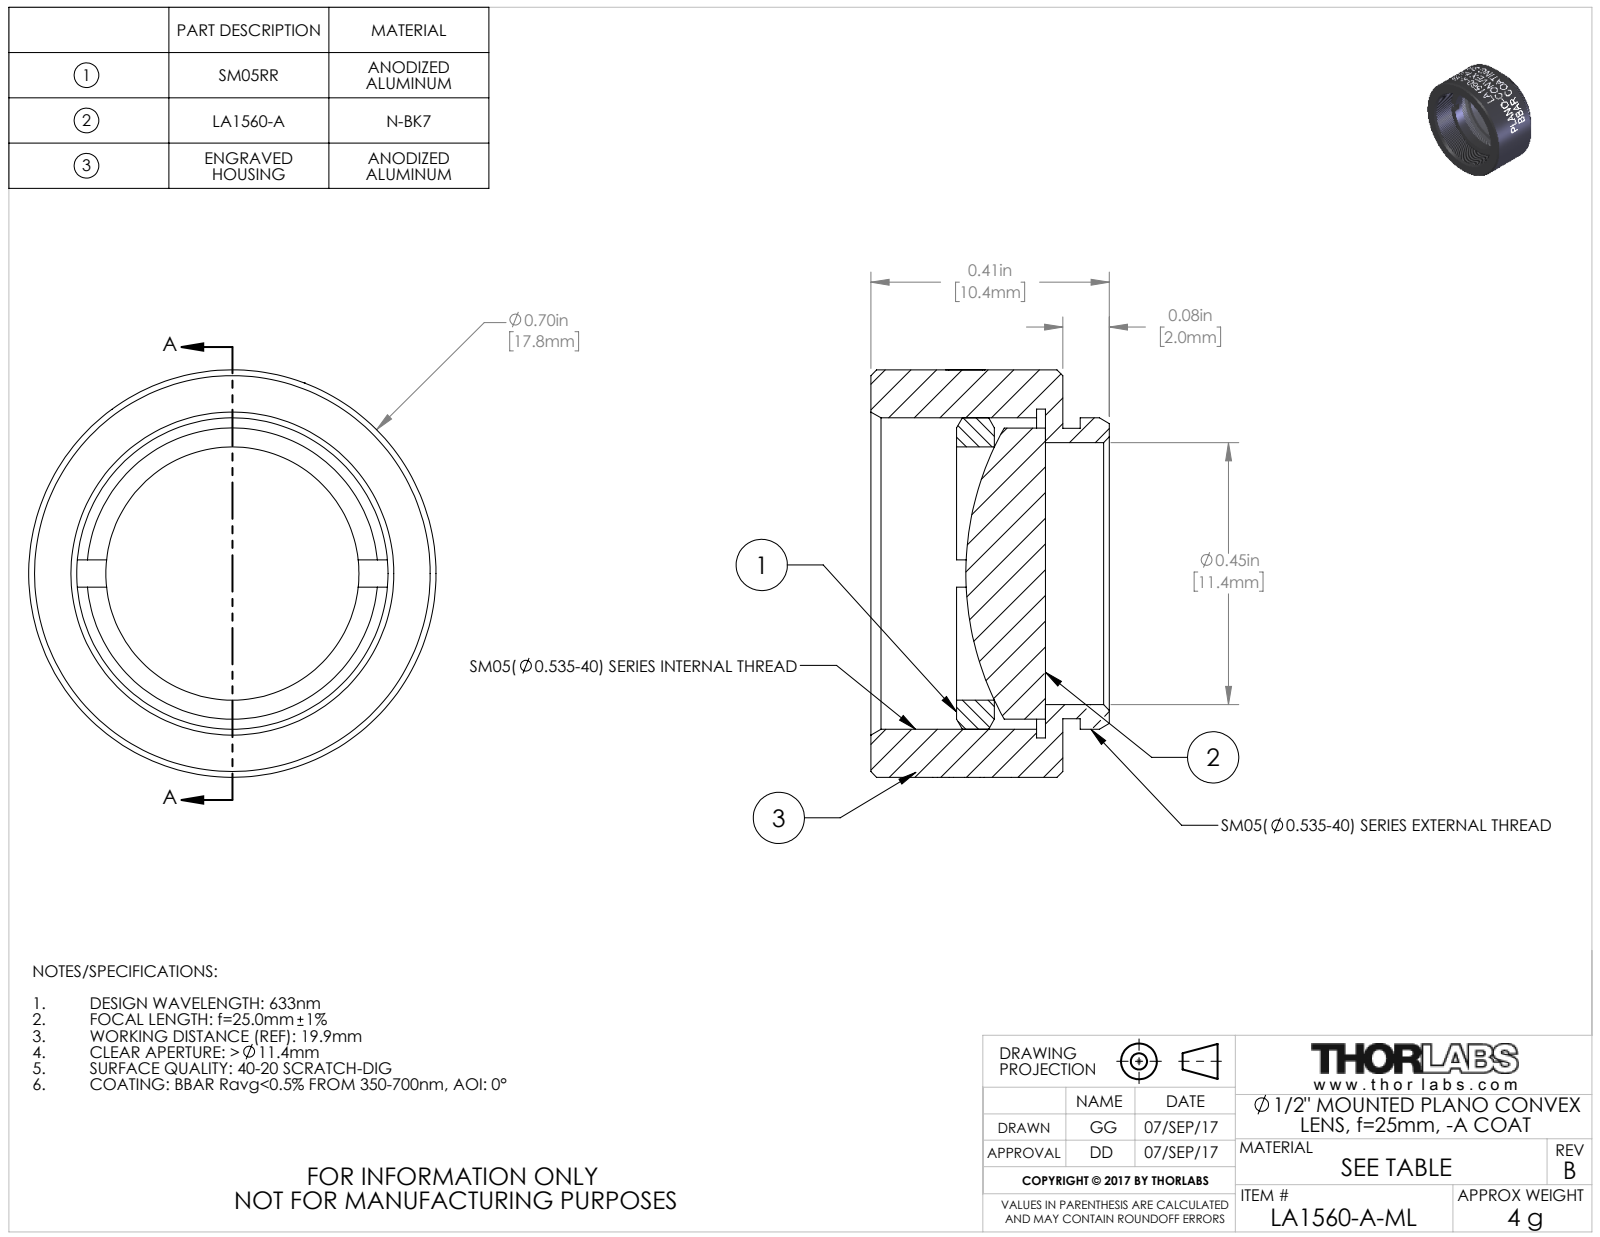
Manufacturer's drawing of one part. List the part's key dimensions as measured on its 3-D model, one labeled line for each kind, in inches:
Part name (STEP PRODUCT): 24395-E0W
STEP written by: SolidWorks 2016 (CONFIG_CONTROL_DESIGN)
Units: inches
Bodies: 3 solids, 275 faces (94 planar, 106 cylindrical, 75 other)
Overall size (bounding box): 0.7 × 0.7 × 0.41
Volume: 0.083 in³ · Surface area: 2.865 in²
Round holes (diameter × count): ⌀0.435 ×1, ⌀0.45 ×1, ⌀0.535 ×1, ⌀0.565 ×1
Round bosses / shafts (diameter × count): ⌀0.7 ×1, ⌀0.535 ×1, ⌀0.5 ×1, ⌀0.499 ×1
Partial cylindrical surfaces — rounded edges, fillets, slot ends (radius × count): R0.35 ×1
Main face-to-face distances: 0.03, 0.3, 0.33, 0.148, 0.213, 0.183, 0.118, 0.087, 0.152, 0.065
